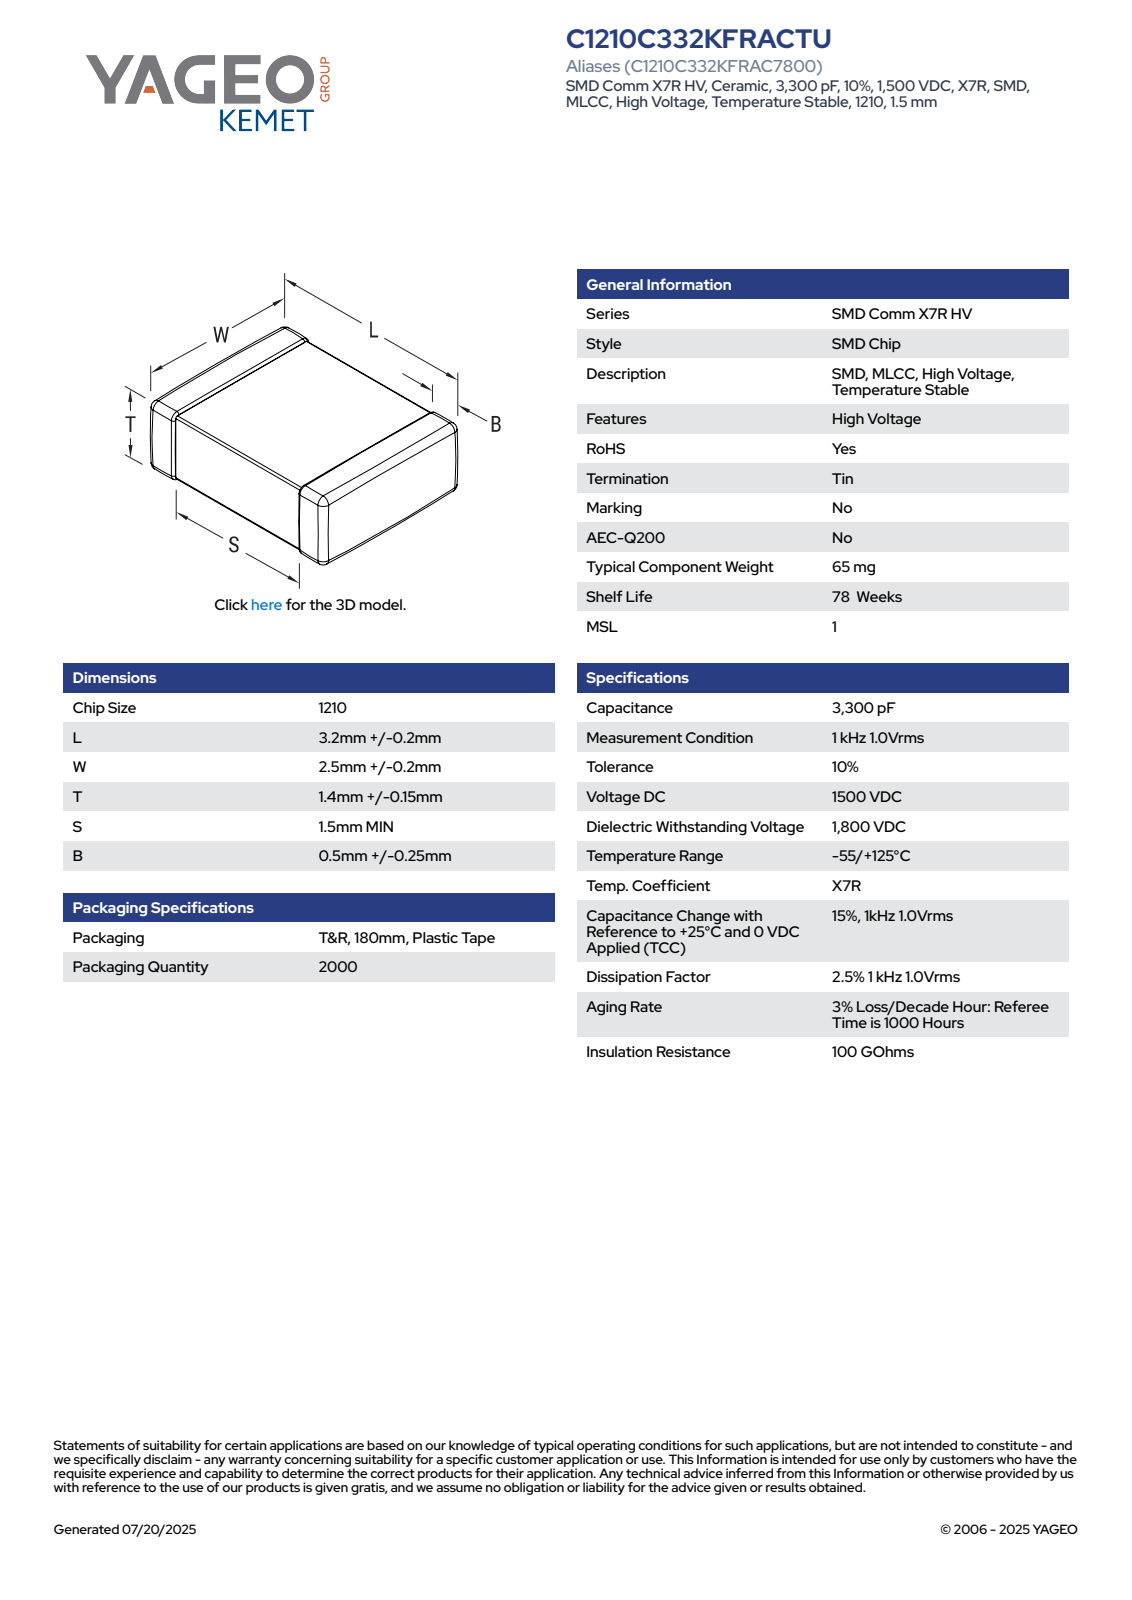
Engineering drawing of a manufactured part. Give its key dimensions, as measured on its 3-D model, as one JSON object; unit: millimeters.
{"part_name": "CCS_CCSTD_1210_L3.4W2.7T1.55B0.5", "step_written_by": "SolidWorks 2021 (AUTOMOTIVE_DESIGN)", "units": "millimeters", "bodies": {"solids": 4, "faces": 125, "planar": 71, "cylindrical": 38, "other": 16}, "overall_size": [3.4, 2.7, 1.55], "volume_mm3": 13, "surface_area_mm2": 37, "face_to_face_distances": [1.49, 1.43, 3.4, 2.64, 1.55, 2.58, 2.7, 1.44, 1.5, 0.4]}
